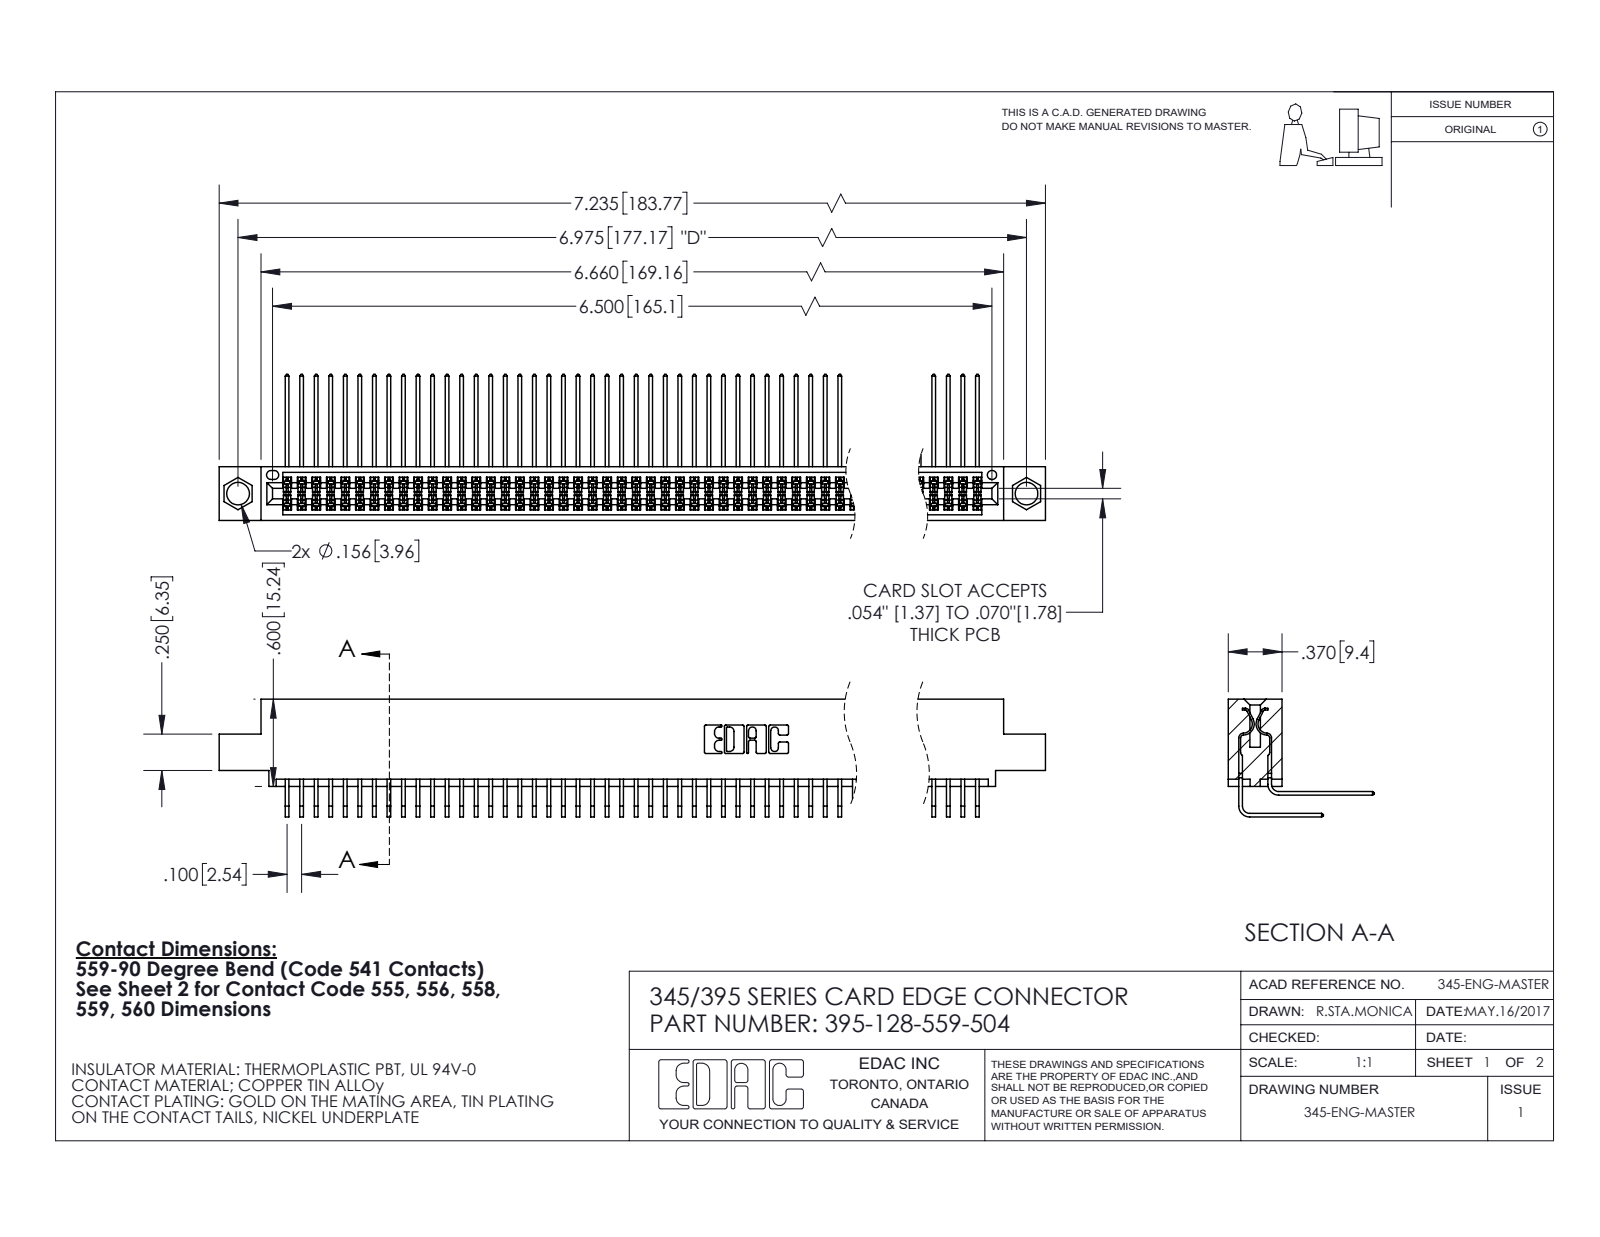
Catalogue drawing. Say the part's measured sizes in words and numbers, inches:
The part is named "345-292-001_558 559 Tail - 1; 345 Part_0.110 Offset - 0.156 Dia-TI; 345-292-001_559 Tail - 2; 395-128-559-504". Its 3-D file was written by "SolidWorks 2020 (CONFIG_CONTROL_DESIGN)". It is 129 solids with 6800 faces: 4578 planar, 2222 cylindrical and 0 other. Overall it measures 7.235 by 1.005 by 0.809 inches. Its volume is 1.136 cubic inches and its surface area 48.61 square inches. Round holes: 2 of diameter 0.156, 1 of diameter 0.064. Partial cylindrical surfaces (rounded edges, fillets, slot ends): 192 of radius 0.006, 22 of radius 0.01, 6 of radius 0.007, 6 of radius 0.031, 3 of radius 0.026, 2 of radius 0.014, 2 of radius 0.019, 2 of radius 0.022. The main face-to-face distances are 0.072, 0.298, 0.2, 0.37, 0.098, 0.272, 0.025, 0.225, 0.175, 0.15. The hole center spacings are 0.27, 6.739, 6.975.
